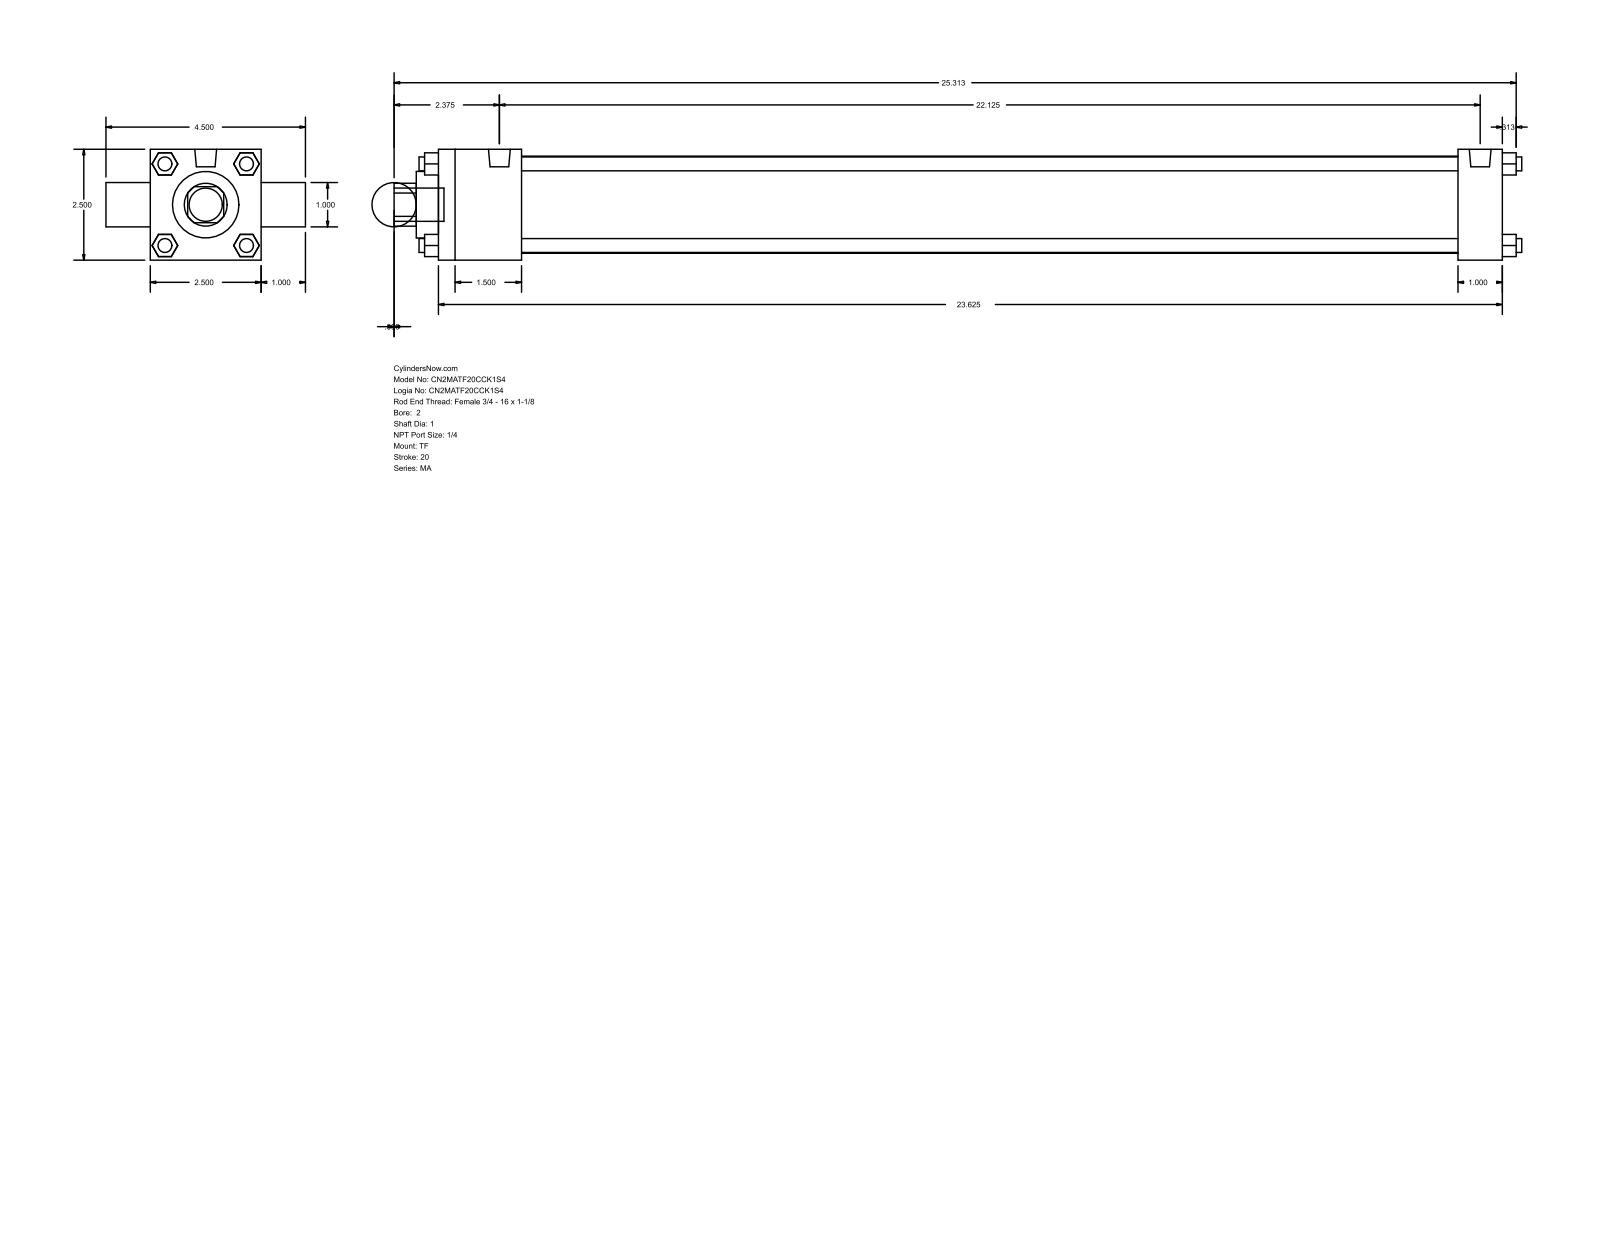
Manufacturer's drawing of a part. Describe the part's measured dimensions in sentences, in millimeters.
The part is named "MA_TF__0200_1". Its 3-D file was written by "GSSL Pune (CONFIG_CONTROL_DESIGN)". It is 0 solids with 120 faces: 92 planar, 28 cylindrical and 0 other. Overall it measures 646.11 by 114.3 by 63.5 millimeters. Round holes: 2 of diameter 25.4, 1 of diameter 38.1, 1 of diameter 55.63. Round bosses or shafts: 7 of diameter 7.94, 2 of diameter 12.49, 1 of diameter 19.05. Partial cylindrical surfaces (rounded edges, fillets, slot ends): 1 of radius 12.29. The main face-to-face distances are 63.5, 25.4, 609.6, 12.7, 47.63, 584.2, 536.57, 561.97, 88.9, 40.47.
